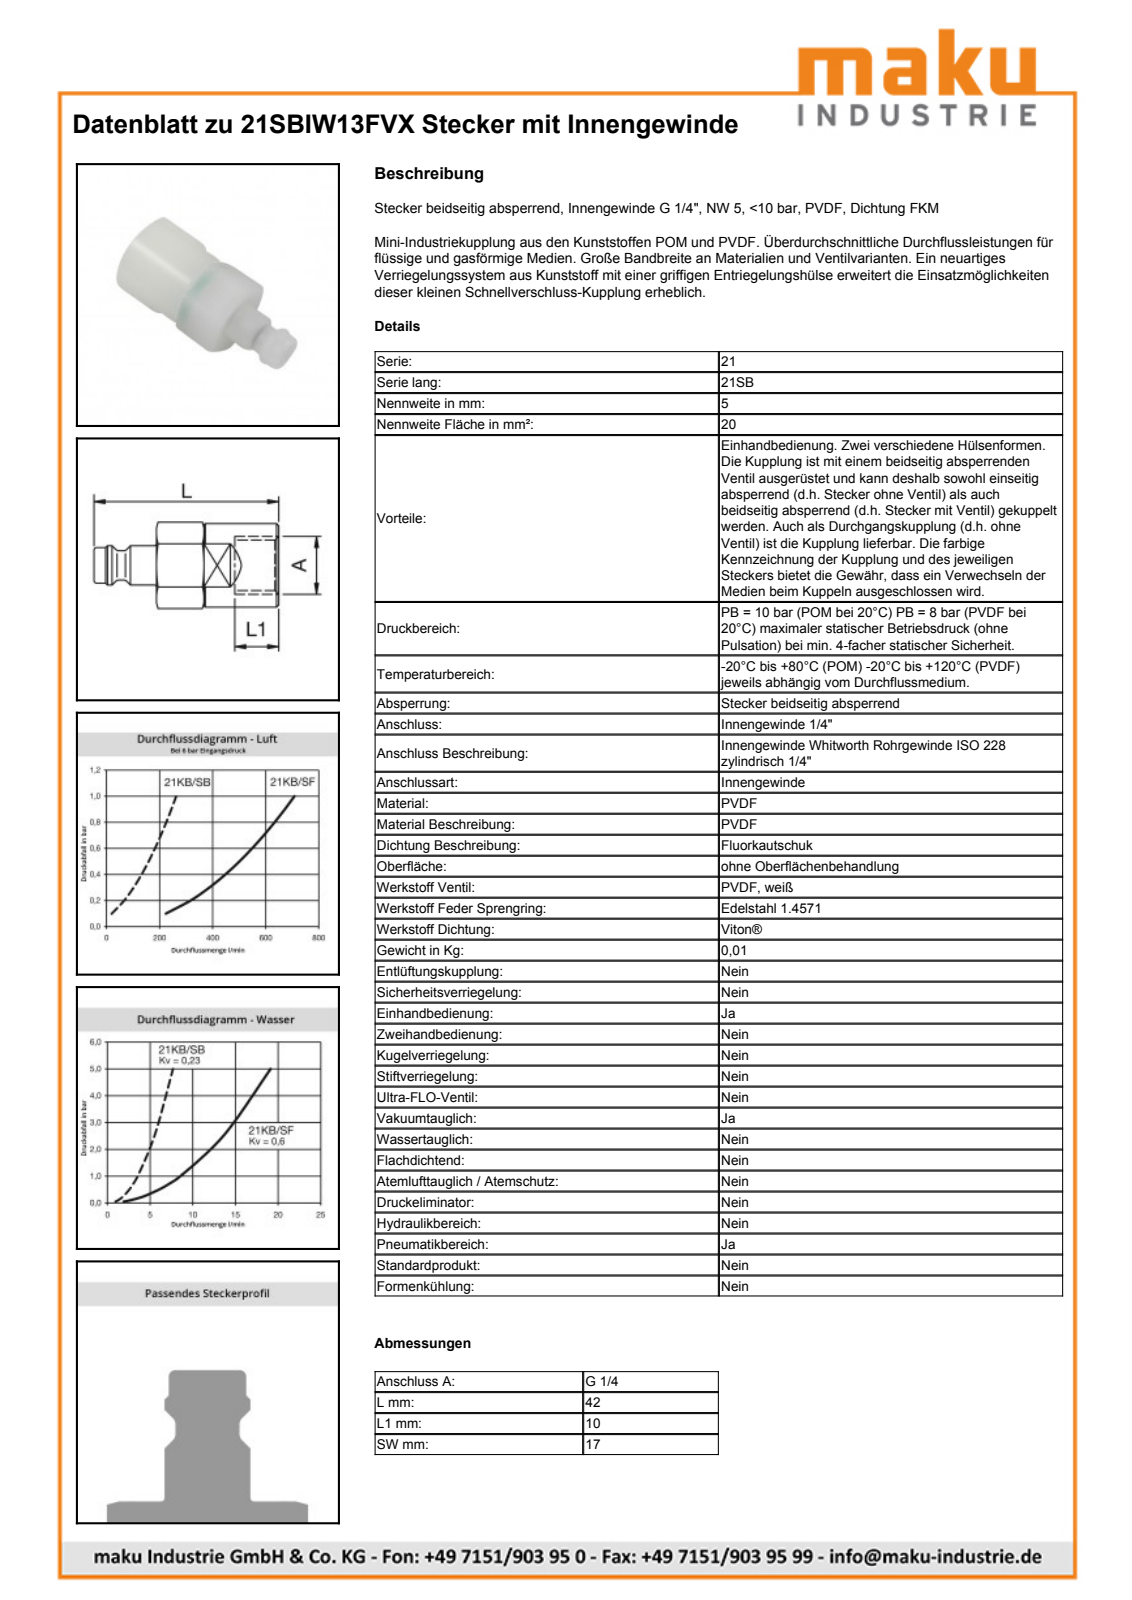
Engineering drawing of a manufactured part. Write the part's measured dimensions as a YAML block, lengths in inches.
part_name: "D106213"
step_written_by: "Autodesk Inventor 2011 (AUTOMOTIVE_DESIGN)"
units: inches
bodies: {solids: 1, faces: 64, planar: 30, cylindrical: 12, other: 22}
overall_size: [1.654, 0.773, 0.748]
volume: 0.424
surface_area: 5.293
round_holes:
  - {diameter: 0.193, count: 1}
  - {diameter: 0.451, count: 1}
  - {diameter: 0.524, count: 1}
  - {diameter: 0.531, count: 1}
round_bosses_or_shafts:
  - {diameter: 0.748, count: 1}
  - {diameter: 0.413, count: 1}
  - {diameter: 0.354, count: 1}
  - {diameter: 0.348, count: 1}
  - {diameter: 0.322, count: 1}
  - {diameter: 0.321, count: 1}
  - {diameter: 0.262, count: 1}
face_to_face_distances: [0.669, 1.096, 0.703, 0.394, 0.984, 0.63, 0.427, 0.276, 0.591, 0.039]
